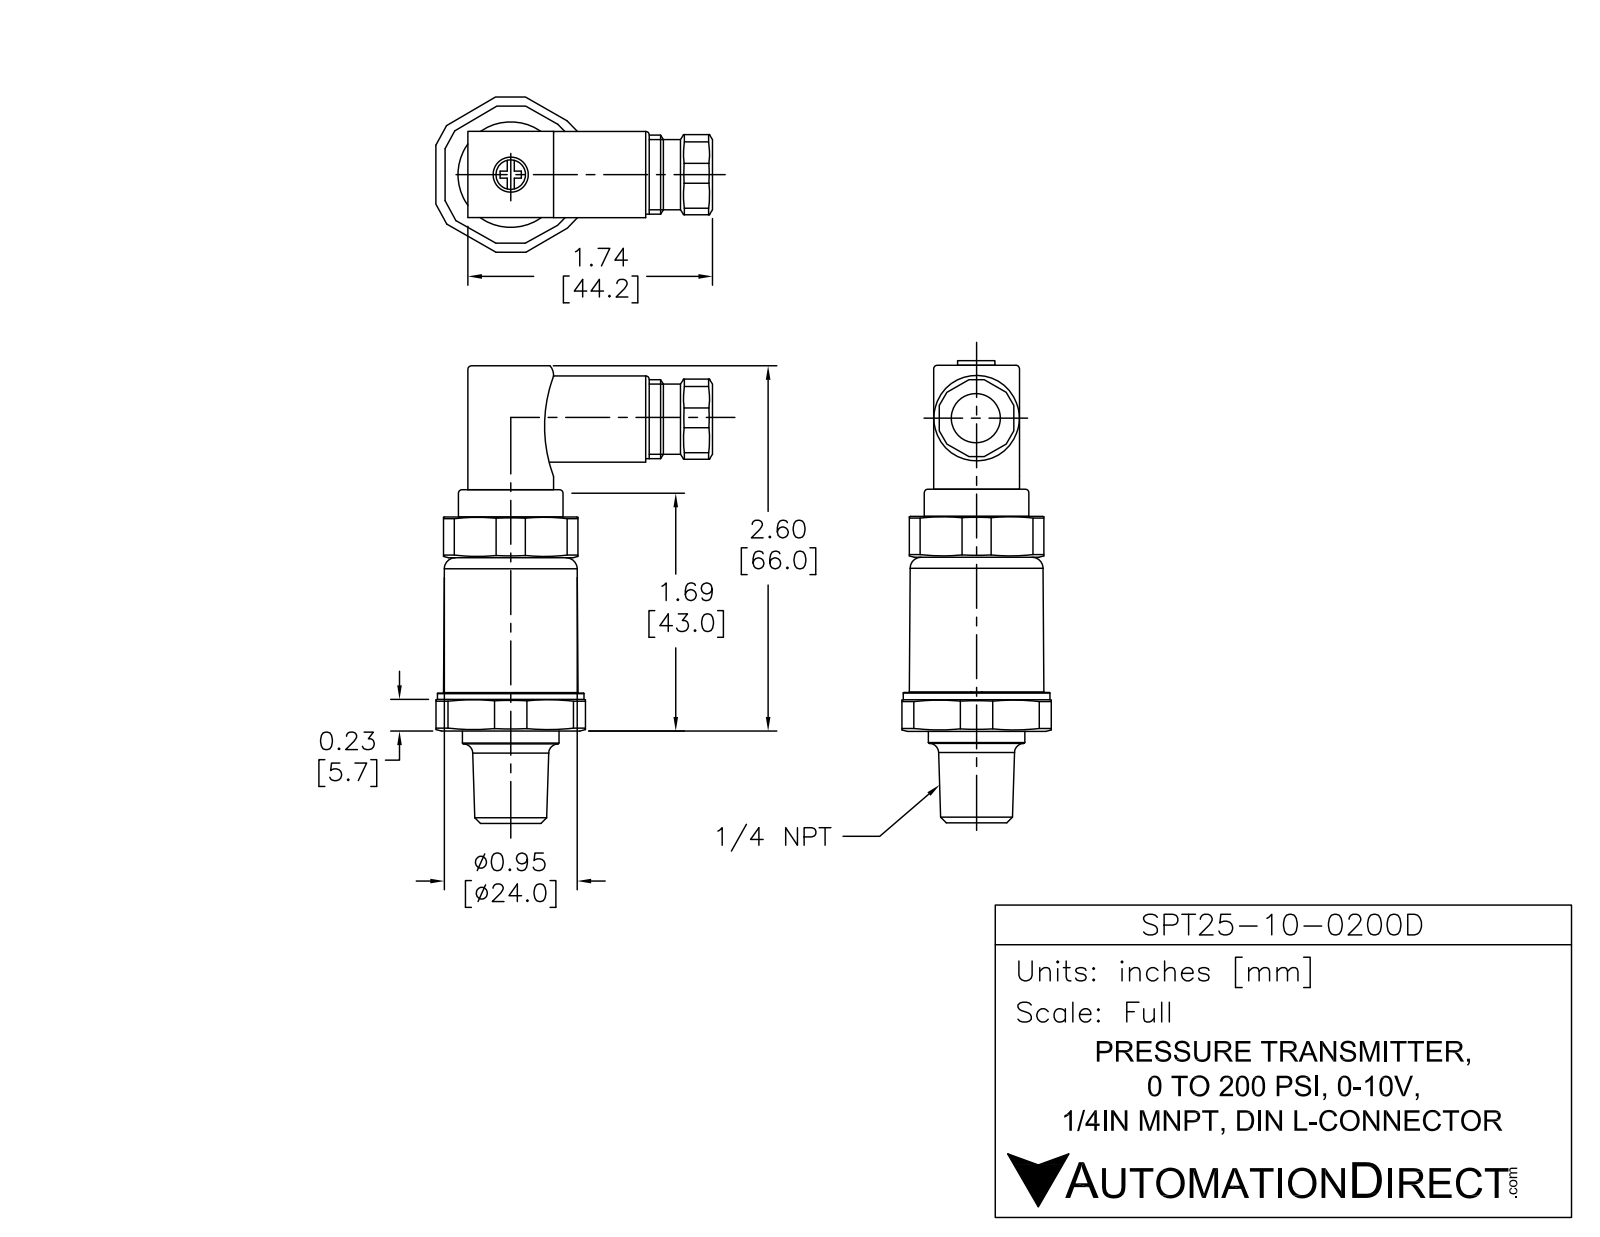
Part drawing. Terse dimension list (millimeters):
name: SPT25-10-0200D
written by: SolidWorks 2011 (AUTOMOTIVE_DESIGN)
unit: mm
bodies: 5 solids, 170 faces (96 planar, 64 cylindrical, 10 other)
size: 81.25 × 38.01 × 35.71
volume: 27 900 mm³; area: 10 134 mm²
holes: 1× ⌀1, 1× ⌀3.3, 1× ⌀7, 1× ⌀8
bosses: 1× ⌀26.75, 1× ⌀24, 1× ⌀17.5, 1× ⌀15, 1× ⌀14, 1× ⌀11
rounds: 8× R1.5, 4× R1.15, 4× R2.25, 3× R2, 1× R1.15, 1× R1.17, 1× R14.5
face distances: 1.5, 29.5, 31, 15.75, 0.35, 15.4, 6.75, 37.75, 36.25, 5
hole spacings: 1.33
